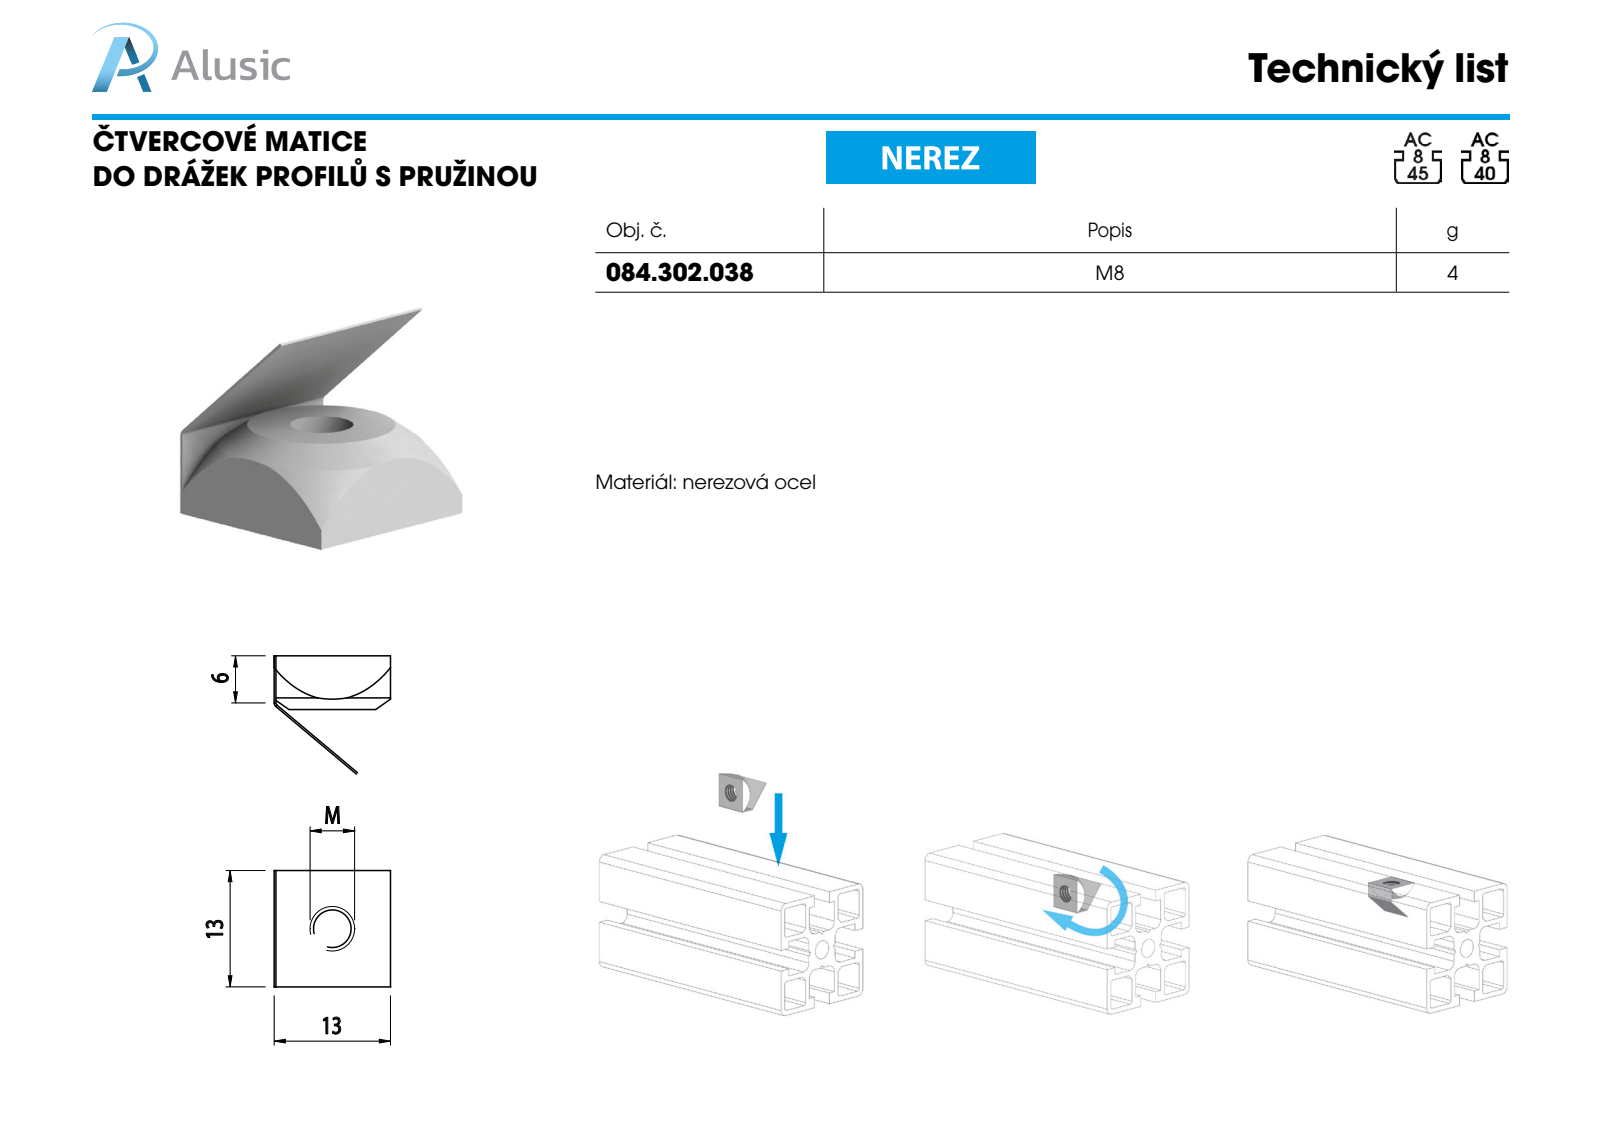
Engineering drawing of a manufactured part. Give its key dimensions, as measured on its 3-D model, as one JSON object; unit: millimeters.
{"part_name": "084.302.038", "step_written_by": "SolidWorks 2016 (CONFIG_CONTROL_DESIGN)", "units": "millimeters", "bodies": {"solids": 2, "faces": 24, "planar": 14, "cylindrical": 4, "other": 6}, "overall_size": [13.21, 13, 13], "volume_mm3": 732, "surface_area_mm2": 1084, "round_holes": [[6.8, 1]], "partial_cylinders_radius": [[0.3, 1], [0.5, 1]], "face_to_face_distances": [13, 12.8, 6]}
